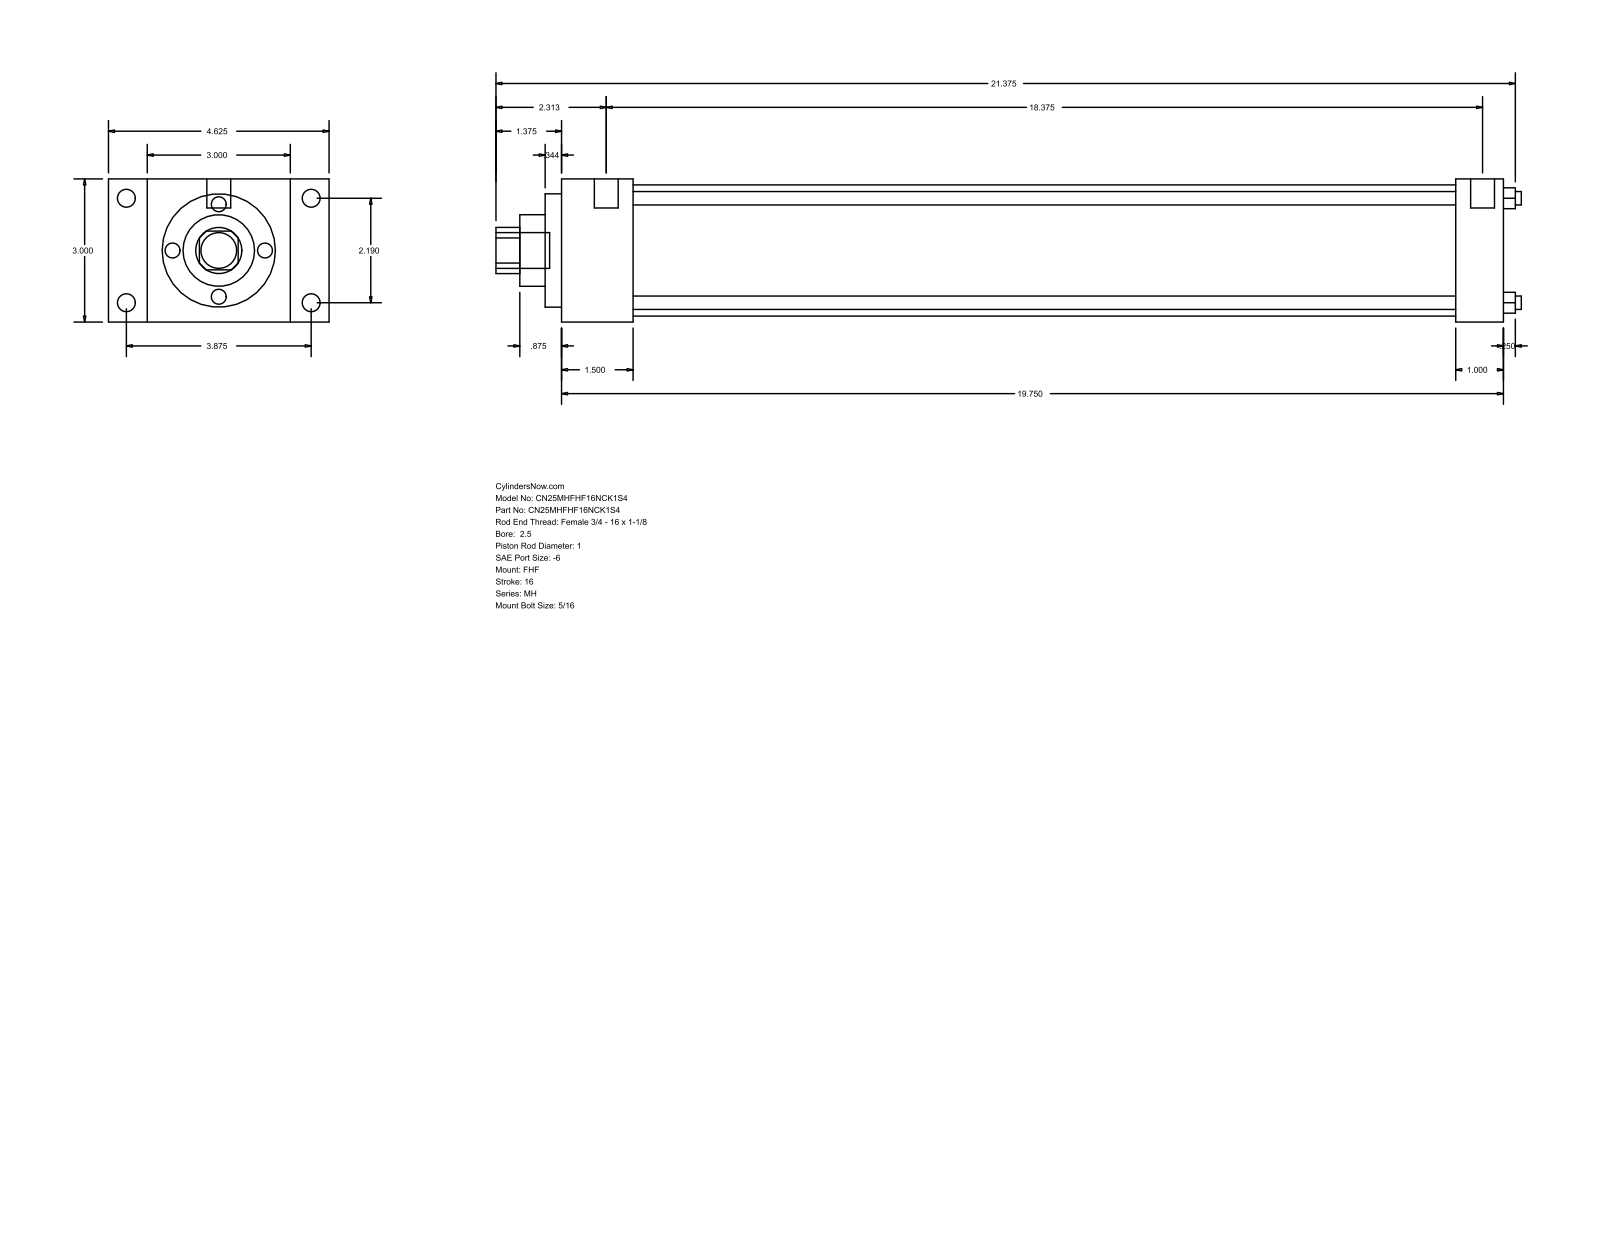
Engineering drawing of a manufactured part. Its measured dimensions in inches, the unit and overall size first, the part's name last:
Units: inches
Overall size (bounding box): 21.5 × 4.625 × 3
Round holes (diameter × count): ⌀0.281 ×4, ⌀1 ×1, ⌀1.5 ×1, ⌀2.375 ×1, ⌀2.75 ×1
Round bosses / shafts (diameter × count): ⌀0.375 ×4, ⌀0.219 ×4, ⌀0.5 ×2, ⌀0.75 ×1
Partial cylindrical surfaces — rounded edges, fillets, slot ends (radius × count): R0.484 ×1
Main face-to-face distances: 3, 19.75, 1.5, 18.25, 0.813, 3.813, 4.625, 18.75, 17.25, 1
Hole centre spacings: 1.548, 2.19, 3.097
Bodies: 0 solids, 90 faces (61 planar, 29 cylindrical, 0 other)
Part name (STEP PRODUCT): MH_FHF__0250_1
STEP written by: GSSL Pune (CONFIG_CONTROL_DESIGN)
